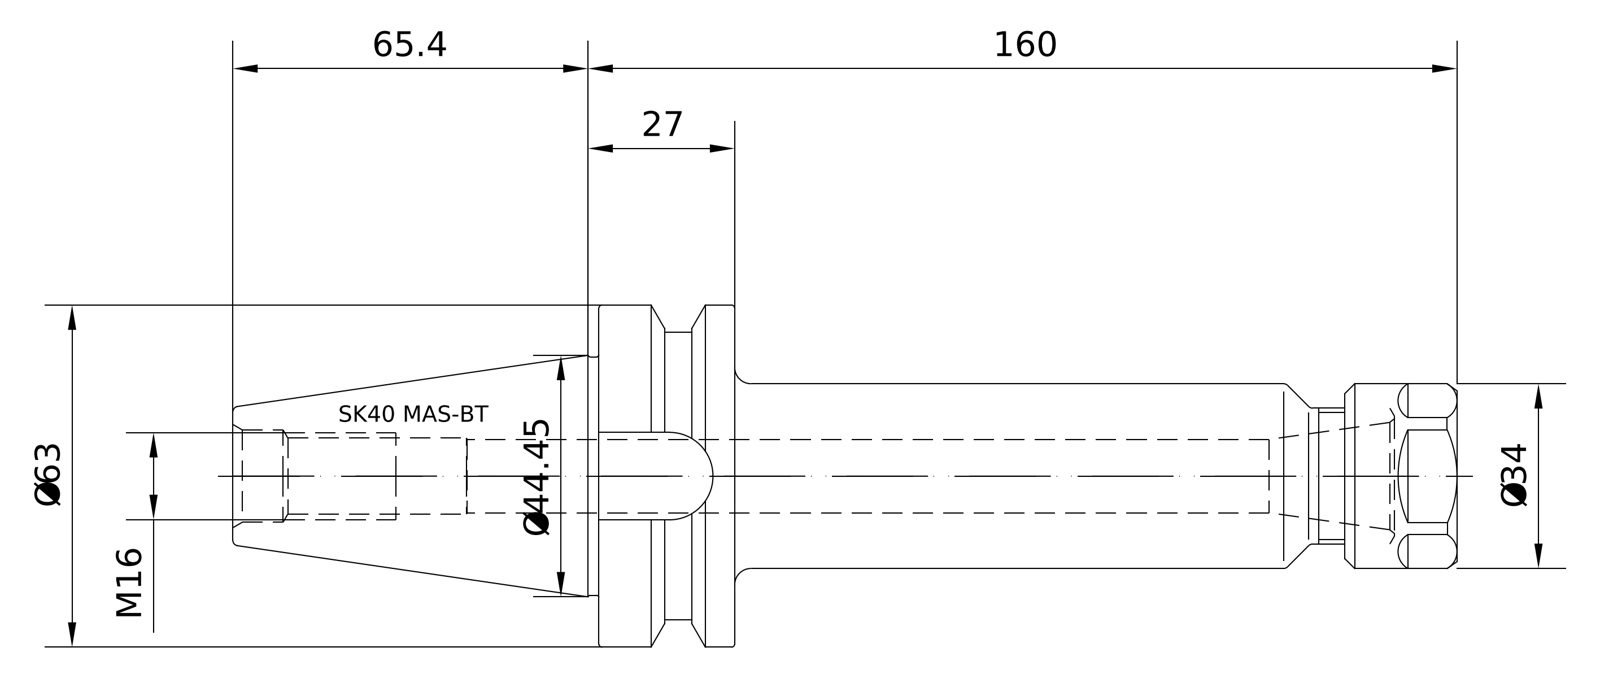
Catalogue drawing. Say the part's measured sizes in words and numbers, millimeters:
The part is named "40-522-20; 83-912-20; 40-522-20_ASM". Its 3-D file was written by "PRO/ENGINEER BY PARAMETRIC TECHNOLOGY CORPORATION, 2010430 (CONFIG_CONTROL_DESIGN)". It is 2 solids with 130 faces: 34 planar, 26 cylindrical and 70 other. Overall it measures 225.4 by 62.98 by 62.98 millimeters. Its volume is 247 623 cubic millimeters and its surface area 38 914 square millimeters. Round holes: 1 of diameter 13.5, 1 of diameter 13.84, 1 of diameter 17.01, 1 of diameter 17.5. Round bosses or shafts: 1 of diameter 62.98, 1 of diameter 52.75, 1 of diameter 43.75, 1 of diameter 34, 1 of diameter 25, 1 of diameter 16.01. Partial cylindrical surfaces (rounded edges, fillets, slot ends): 1 of radius 8.1. The main face-to-face distances are 25, 139, 114, 30, 158, 133, 19, 7.45, 37.45, 44.9.
